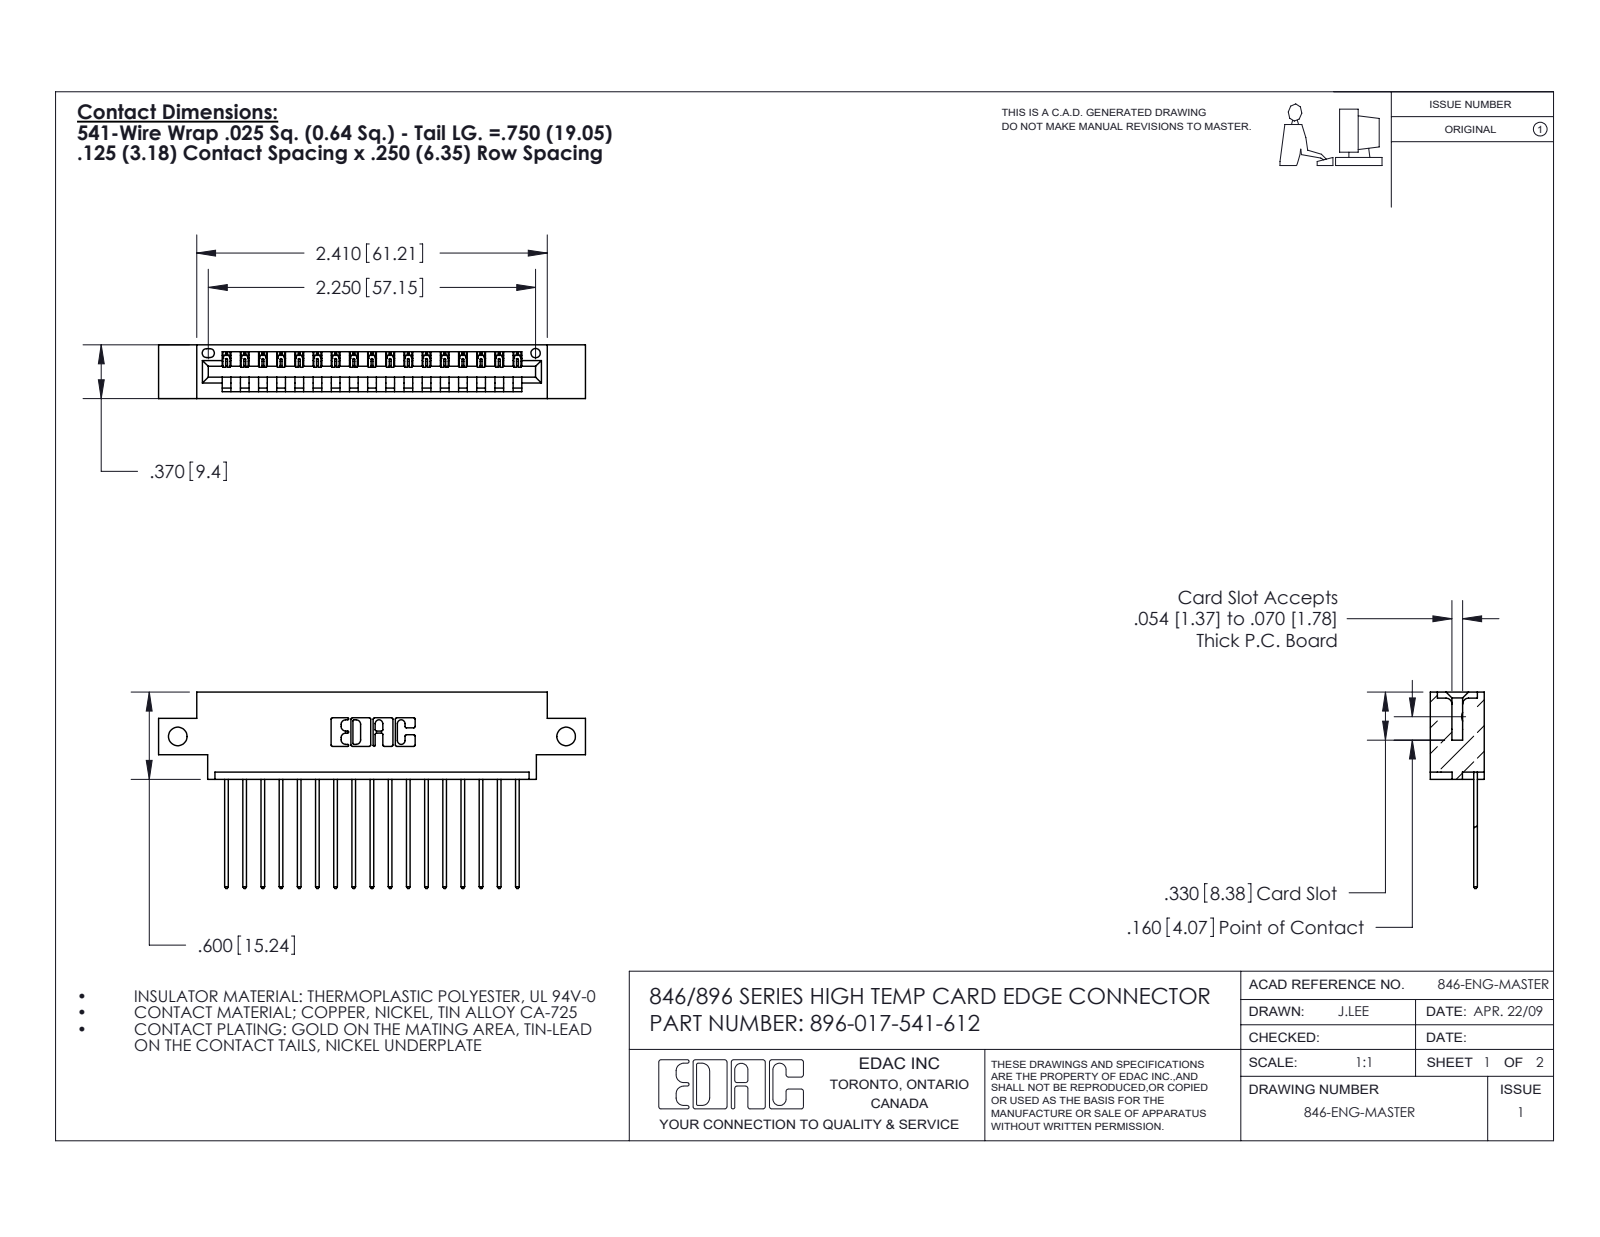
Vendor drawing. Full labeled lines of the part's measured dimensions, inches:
Part name (STEP PRODUCT): 346 Part_0.170 Offset - Side Mount; 345-292-001_345-293-141; 396-017-541-612
STEP written by: SolidWorks 2016 (CONFIG_CONTROL_DESIGN)
Units: inches
Bodies: 18 solids, 1112 faces (760 planar, 352 cylindrical, 0 other)
Overall size (bounding box): 2.935 × 1.35 × 0.37
Volume: 0.414 in³ · Surface area: 13.25 in²
Round holes (diameter × count): ⌀0.128 ×2, ⌀0.064 ×1
Partial cylindrical surfaces — rounded edges, fillets, slot ends (radius × count): R0.006 ×34, R0.01 ×34, R0.01 ×22, R0.007 ×6, R0.031 ×6, R0.026 ×3, R0.031 ×2, R0.04 ×2
Main face-to-face distances: 0.048, 0.322, 0.37, 0.25, 0.072, 0.298, 0.025, 0.148, 0.222, 0.1
Hole centre spacings: 2.67
